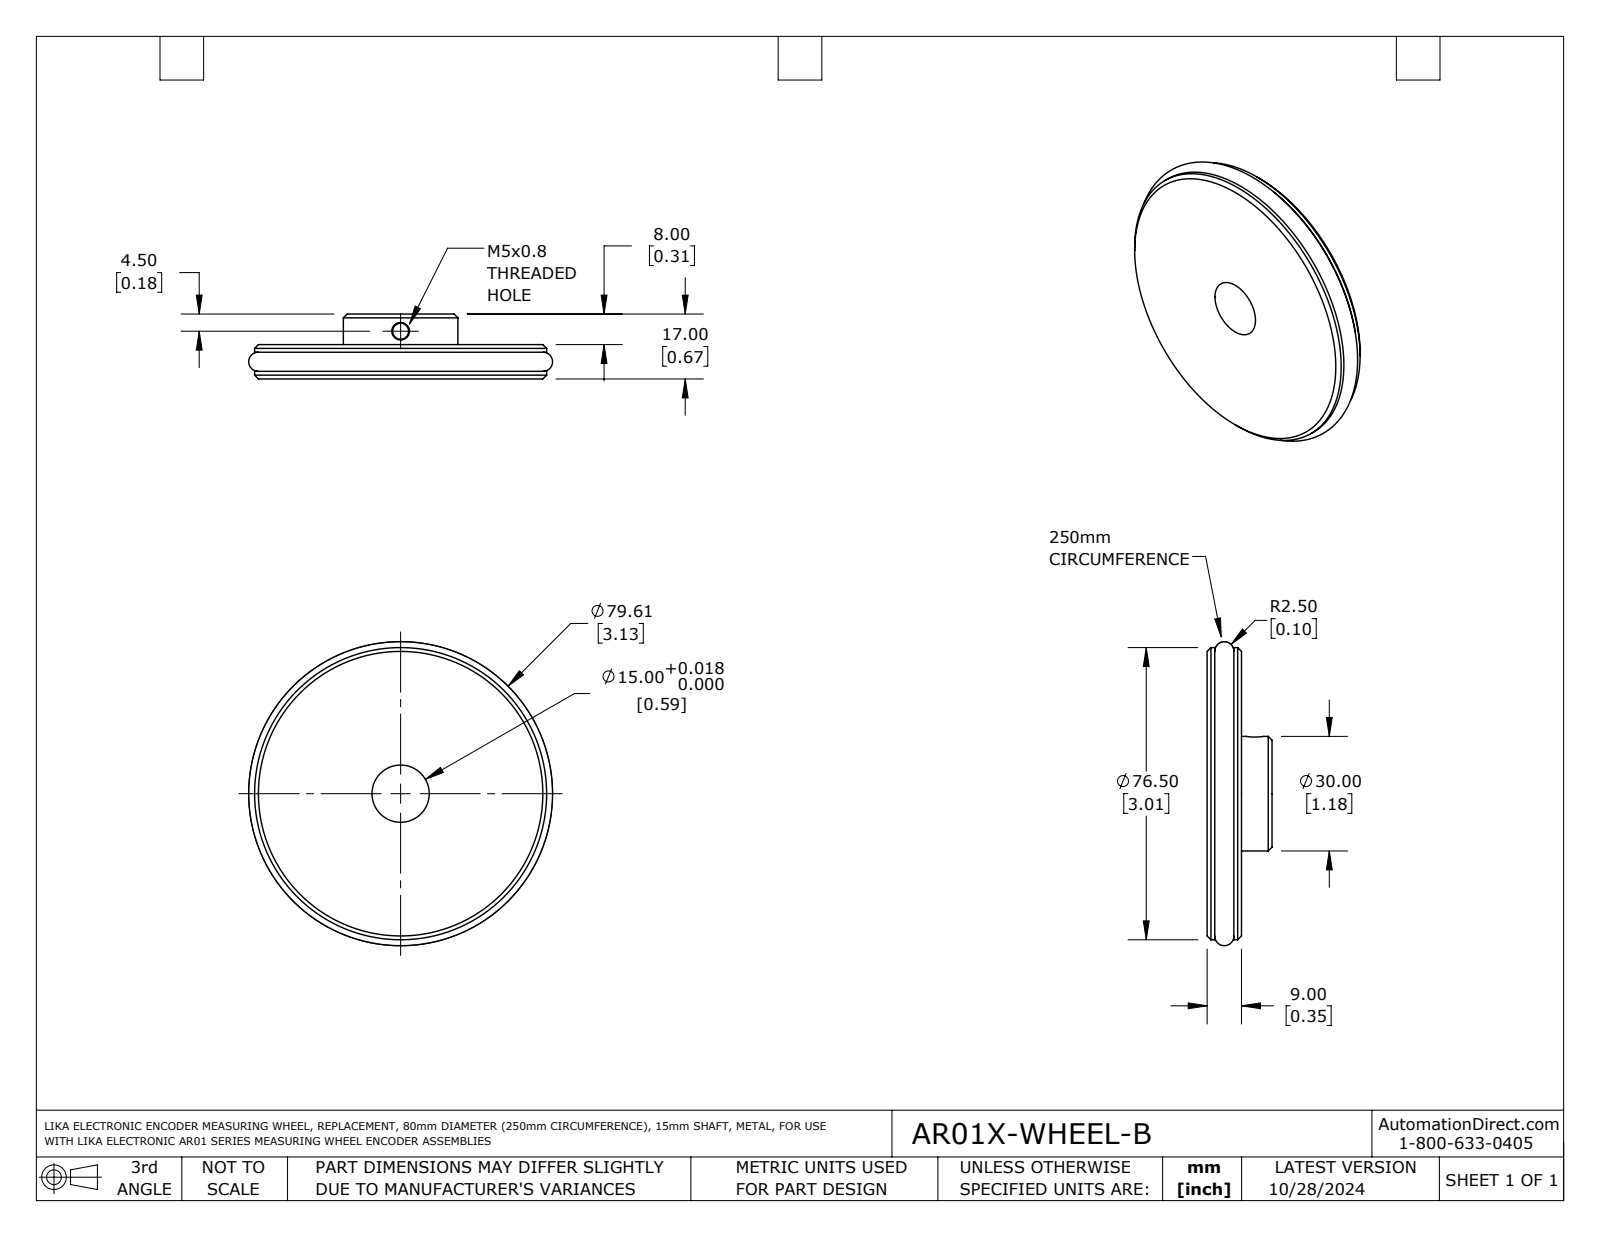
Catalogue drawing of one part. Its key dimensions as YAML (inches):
part_name: "AR01X-WHEEL-B"
step_written_by: "SolidWorks 2021 (AUTOMOTIVE_DESIGN)"
units: inches
bodies: {solids: 2, faces: 40, planar: 6, cylindrical: 14, other: 20}
overall_size: [3.134, 3.134, 0.669]
volume: 2.098
surface_area: 28.4
round_holes:
  - {diameter: 0.165, count: 1}
  - {diameter: 0.591, count: 1}
  - {diameter: 2.362, count: 1}
round_bosses_or_shafts:
  - {diameter: 3.012, count: 1}
  - {diameter: 2.736, count: 1}
  - {diameter: 1.181, count: 1}
face_to_face_distances: [0.197, 0.354, 0.157, 0.079, 0.276, 0.315, 0.512, 0.669, 0.394, 0.118]
